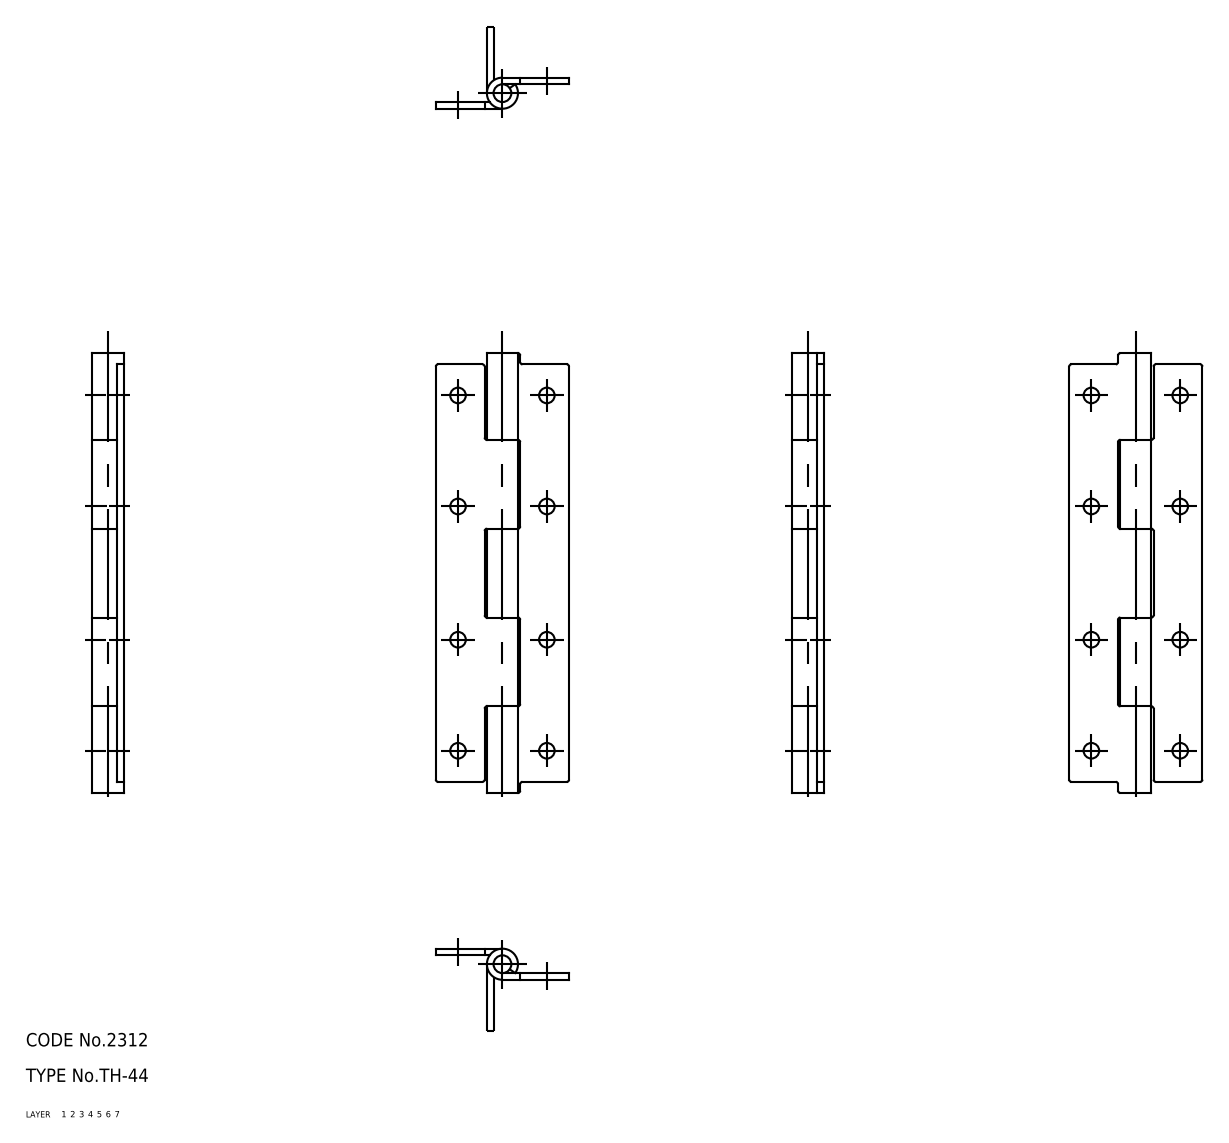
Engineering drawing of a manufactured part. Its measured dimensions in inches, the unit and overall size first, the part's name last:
Units: inches
Overall size (bounding box): 3.898 × 1.181 × 0.276
Volume: 0.427 in³ · Surface area: 15.47 in²
Bodies: 3 solids, 80 faces (0 planar, 0 cylindrical, 80 other)
Part name (STEP PRODUCT): shaft; hinge piece_B; hinge piece_A; TH_44_9372_36
STEP written by: CADfix (AUTOMOTIVE_DESIGN)
